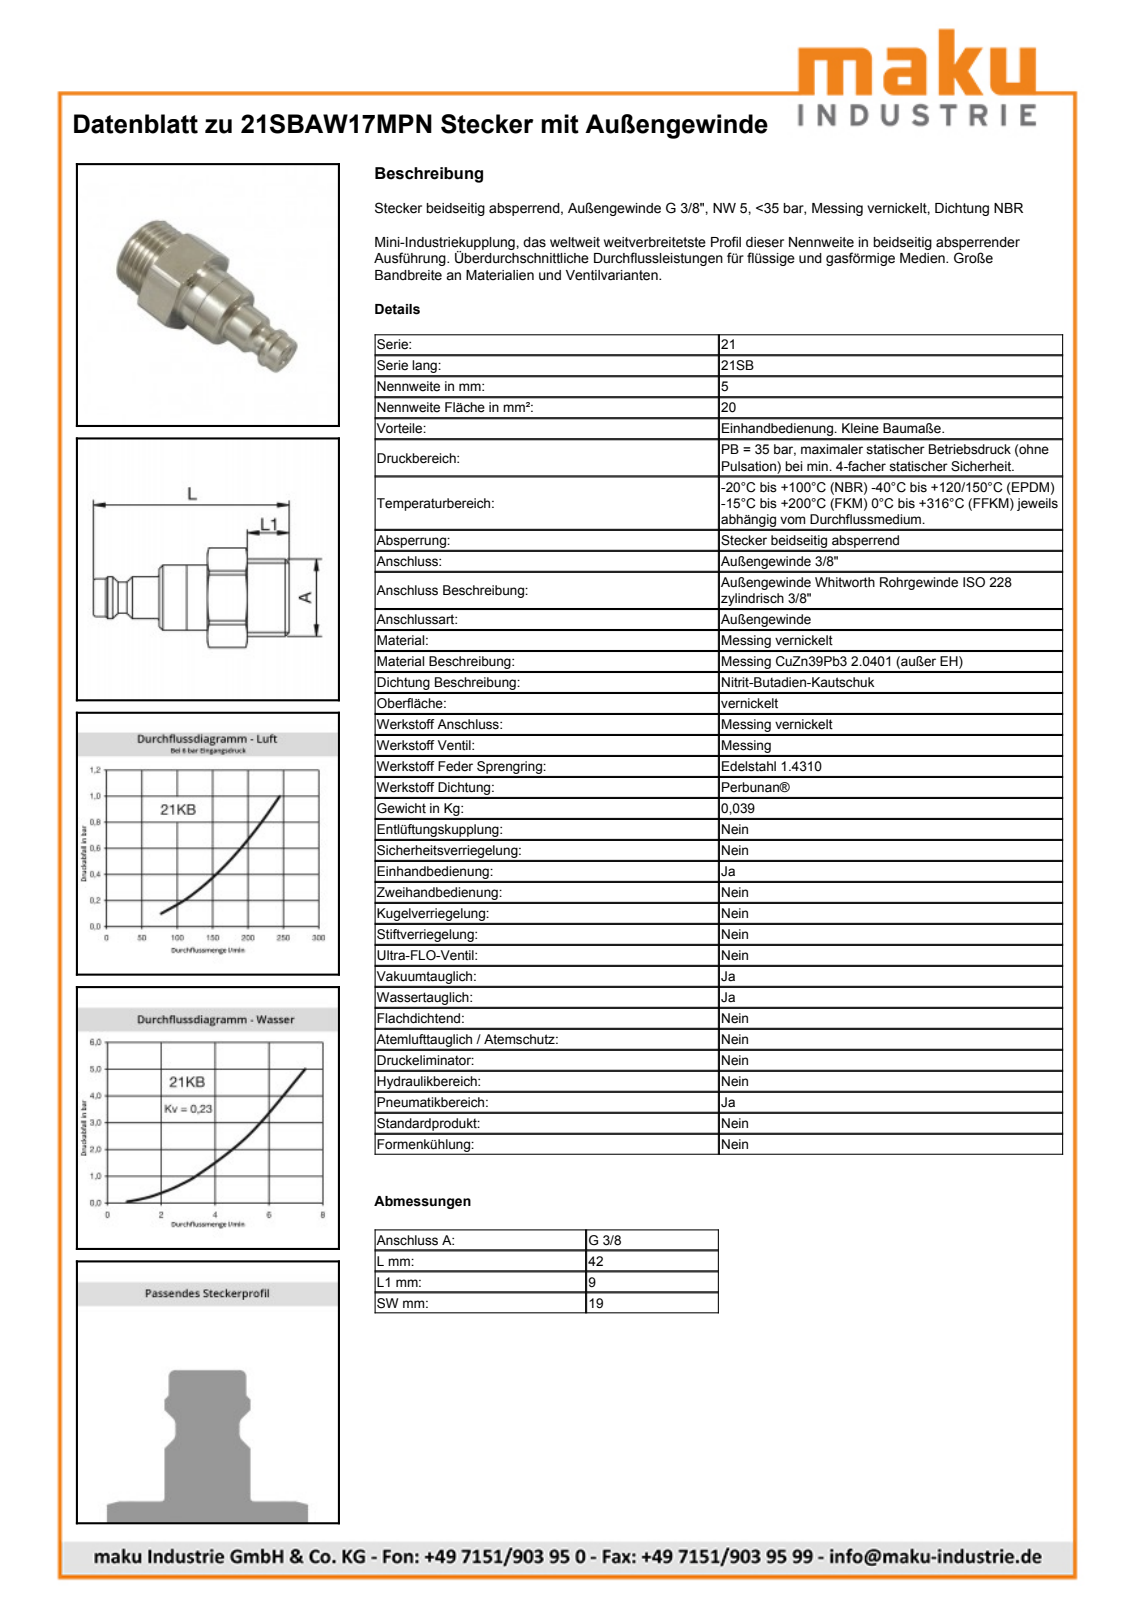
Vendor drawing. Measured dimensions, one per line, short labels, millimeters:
name: D105847
written by: Autodesk Inventor 2011 (AUTOMOTIVE_DESIGN)
unit: mm
bodies: 1 solid, 44 faces (11 planar, 12 cylindrical, 21 other)
size: 42 × 21.4 × 19.56
volume: 6 955 mm³; area: 2 413 mm²
bosses: 1× ⌀16.66, 1× ⌀14, 1× ⌀9, 1× ⌀8.1, 1× ⌀6.65
rounds: 1× R10.7
face distances: 19, 17.55, 8.55, 9, 10.35, 18.9, 27.9, 14.1, 24.45, 33
